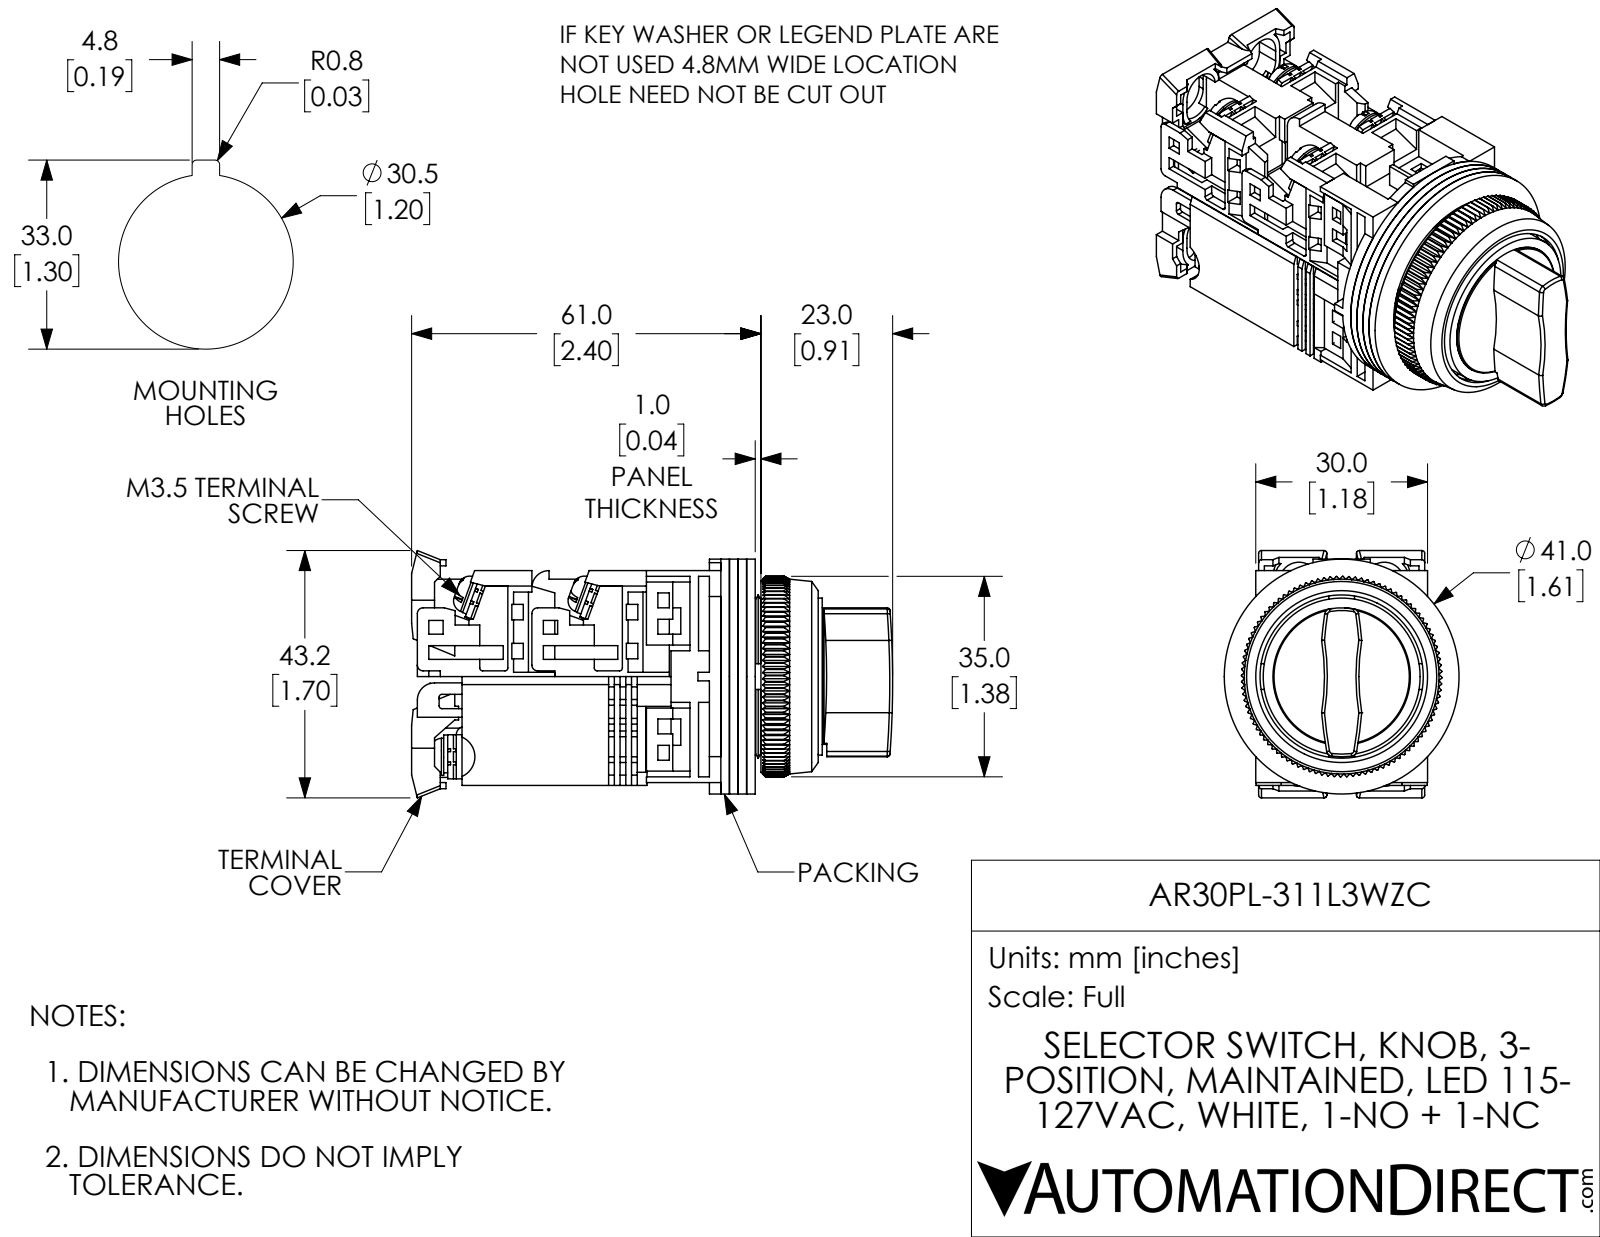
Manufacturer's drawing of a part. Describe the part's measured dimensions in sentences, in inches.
The part is named "AR30PL-311L3WZC". Its 3-D file was written by "SolidWorks 2017 (AUTOMOTIVE_DESIGN)". It is 34 solids with 2724 faces: 2033 planar, 354 cylindrical and 337 other. Overall it measures 3.307 by 1.7 by 1.614 inches. Its volume is 3.442 cubic inches and its surface area 70.72 square inches. Round holes: 8 of diameter 0.138, 6 of diameter 0.142, 3 of diameter 0.118, 1 of diameter 0.472, 1 of diameter 0.709, 1 of diameter 0.768, 1 of diameter 0.827, 1 of diameter 1.122, 1 of diameter 1.181, 1 of diameter 1.252. Round bosses or shafts: 6 of diameter 0.26, 4 of diameter 0.138, 2 of diameter 0.063, 1 of diameter 1.614, 1 of diameter 1.15, 1 of diameter 1.079, 1 of diameter 0.945, 1 of diameter 0.886. Partial cylindrical surfaces (rounded edges, fillets, slot ends): 25 of radius 0.059, 15 of radius 0.02, 8 of radius 0.039, 4 of radius 0.138, 4 of radius 0.177, 3 of radius 0.118, 2 of radius 1.575, 2 of radius 2.953. The main face-to-face distances are 0.059, 0.118, 0.177, 0.039, 0.748, 0.079, 0.787, 0.063, 0.689, 0.197. The hole center spacings are 0.579, 0.269, 0.638, 0.297, 0.624, 0.02, 0.302, 0.583.
